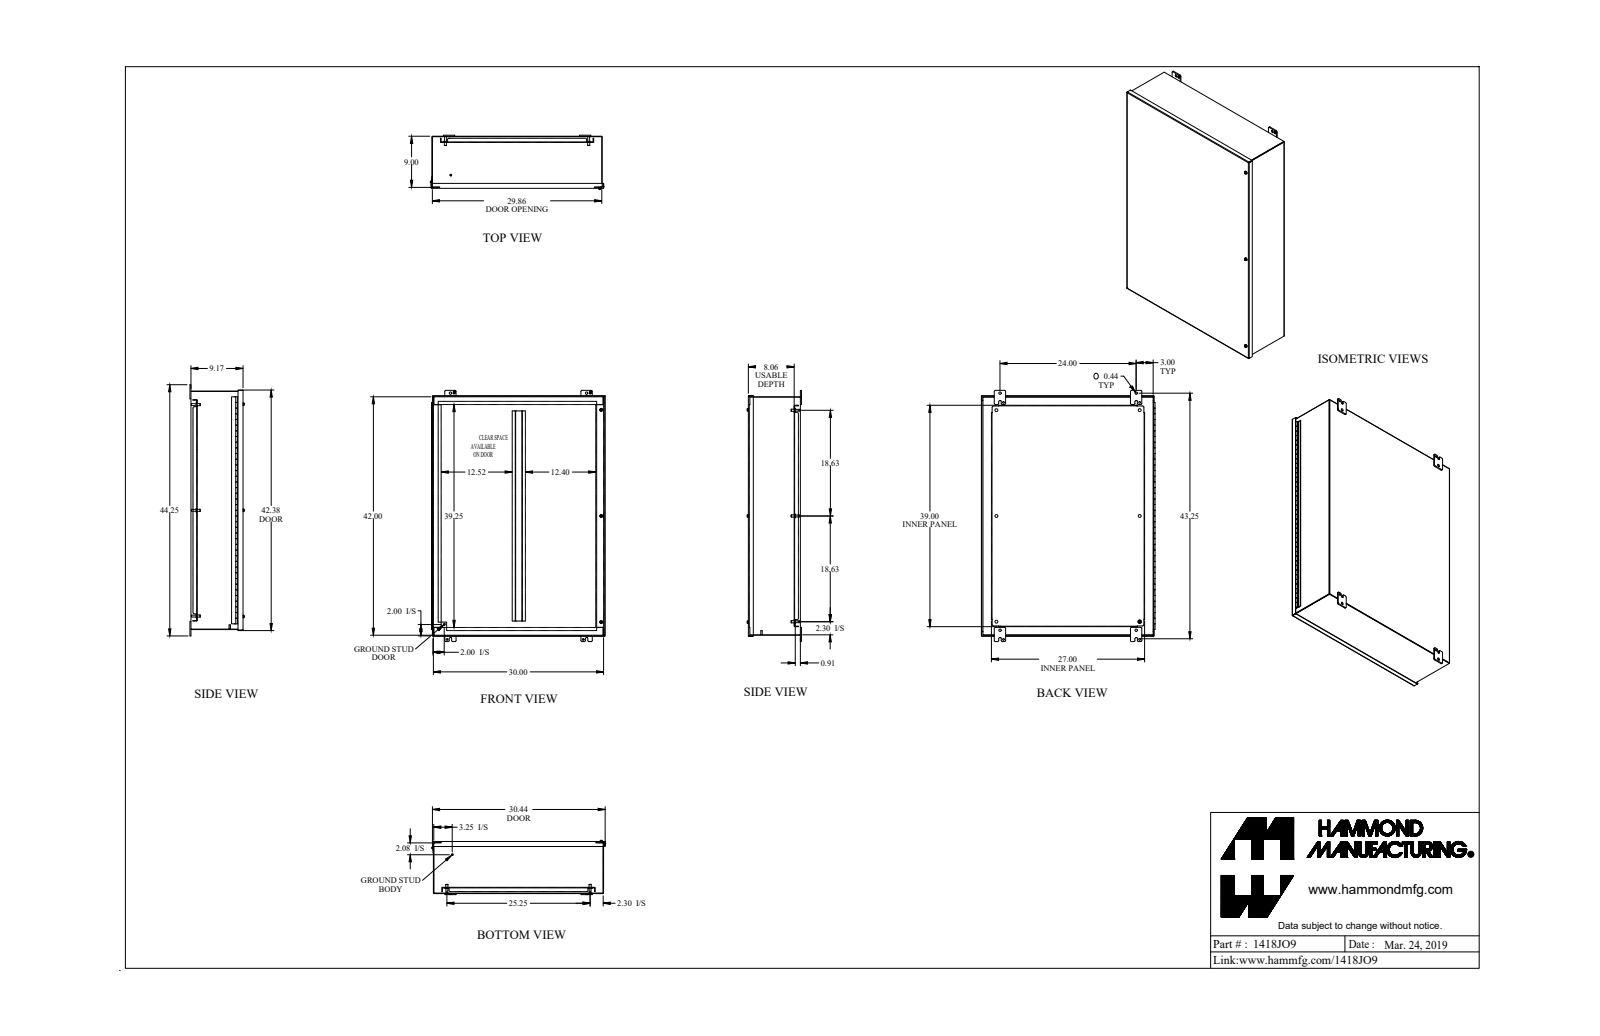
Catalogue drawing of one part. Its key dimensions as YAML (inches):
part_name: "1418JO9_Default"
step_written_by: "SolidWorks 2018 (CONFIG_CONTROL_DESIGN)"
units: inches
bodies: {solids: 48, faces: 1327, planar: 782, cylindrical: 483, other: 62}
overall_size: [44.25, 30.604, 9.571]
volume: 476.6
surface_area: 11985
round_holes:
  - {diameter: 0.313, count: 7}
  - {diameter: 0.5, count: 6}
  - {diameter: 0.307, count: 4}
  - {diameter: 0.437, count: 4}
  - {diameter: 0.445, count: 4}
  - {diameter: 0.26, count: 3}
  - {diameter: 0.266, count: 3}
  - {diameter: 0.28, count: 3}
  - {diameter: 0.29, count: 3}
  - {diameter: 0.397, count: 3}
  - {diameter: 0.187, count: 1}
  - {diameter: 3.5, count: 1}
round_bosses_or_shafts:
  - {diameter: 0.65, count: 6}
  - {diameter: 0.375, count: 6}
  - {diameter: 0.33, count: 6}
  - {diameter: 1, count: 4}
  - {diameter: 0.51, count: 3}
  - {diameter: 0.5, count: 3}
  - {diameter: 0.39, count: 3}
  - {diameter: 0.244, count: 3}
partial_cylinders:
  - {radius: 0.188, count: 36}
  - {radius: 0.25, count: 28}
  - {radius: 0.116, count: 16}
  - {radius: 0.036, count: 10}
  - {radius: 0.108, count: 10}
  - {radius: 0.218, count: 8}
  - {radius: 0.125, count: 7}
  - {radius: 0.133, count: 6}
face_to_face_distances: [0.072, 9.1, 9.028, 9.172, 0.095, 1.104, 1.032, 7.996, 8.068, 1.009]
hole_center_spacings: [37.25, 45.002, 1.735, 3.065, 18.625, 18.687, 18.688, 24]
